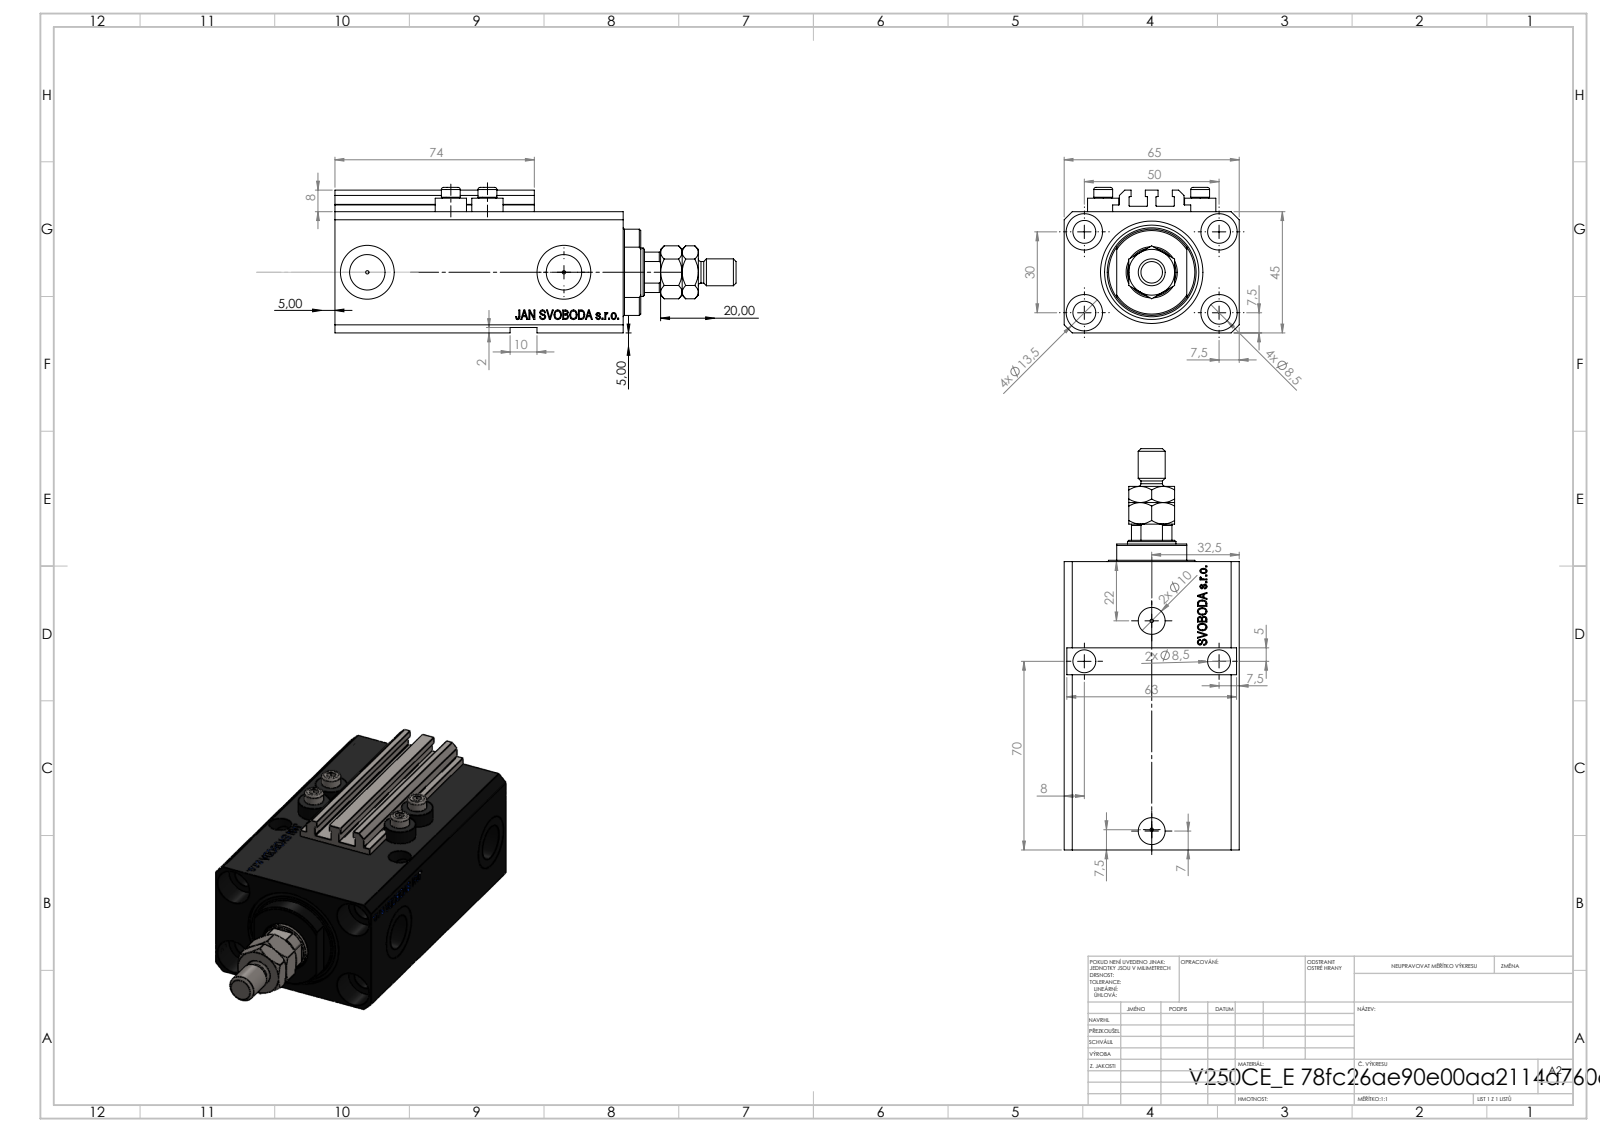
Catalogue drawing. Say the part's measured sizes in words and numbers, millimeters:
The part is named "V250CE_C_VCP; MTA; V250CE_E_Body; V250CE_VC_E (+1 more)". Its 3-D file was written by "SolidWorks 2019 (CONFIG_CONTROL_DESIGN)". It is 9 solids with 1152 faces: 530 planar, 162 cylindrical and 460 other. Overall it measures 149 by 65 by 54 millimeters. Its volume is 274 269 cubic millimeters and its surface area 79 751 square millimeters. Round holes: 9 of diameter 8.5, 4 of diameter 1.25, 4 of diameter 4, 4 of diameter 13.5, 2 of diameter 10, 2 of diameter 13.16, 2 of diameter 20, 1 of diameter 18, 1 of diameter 25, 1 of diameter 38. Round bosses or shafts: 4 of diameter 11.6, 4 of diameter 7, 1 of diameter 10, 1 of diameter 8. Partial cylindrical surfaces (rounded edges, fillets, slot ends): 10 of radius 0.2, 1 of radius 8.5, 1 of radius 16. The main face-to-face distances are 45, 65, 14, 93, 2, 47, 107, 6.9, 20.5, 24. The hole center spacings are 29.15, 50, 13.6, 14.76, 15.12, 27.51, 27.89, 30.
